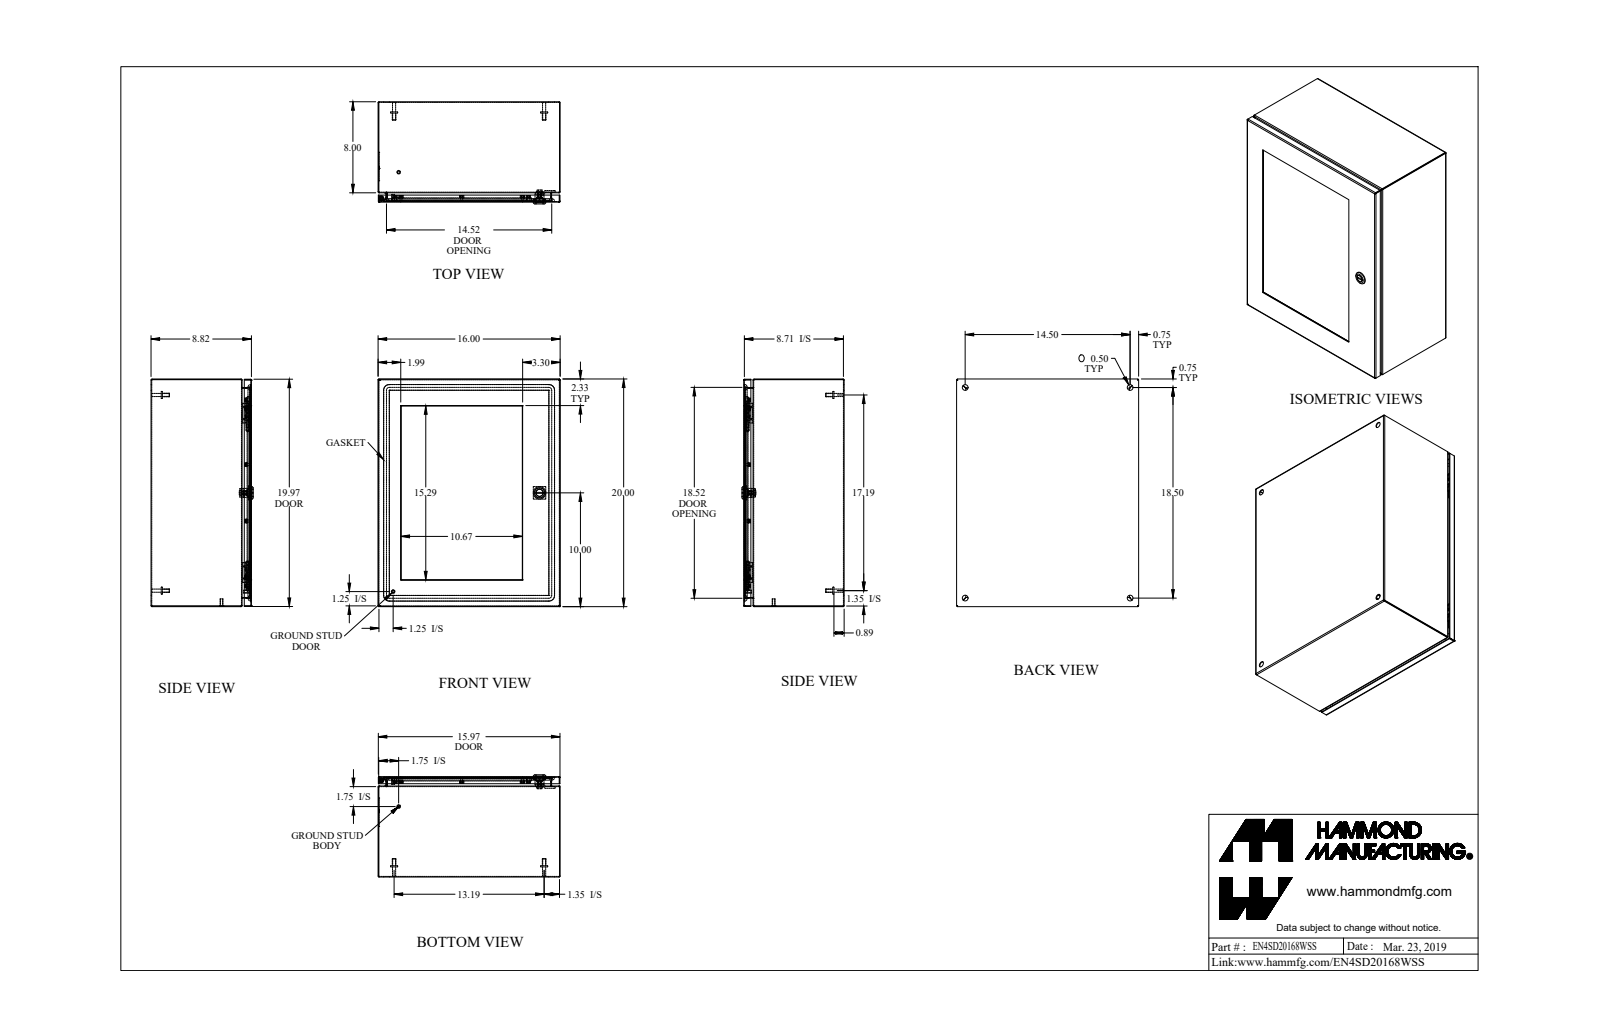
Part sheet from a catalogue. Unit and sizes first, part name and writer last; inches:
Units: inches
Overall size (bounding box): 20 × 16 × 8.982
Round holes (diameter × count): ⌀0.13 ×14, ⌀0.25 ×14, ⌀0.5 ×5, ⌀0.172 ×1, ⌀0.197 ×1, ⌀0.24 ×1, ⌀0.242 ×1, ⌀0.387 ×1, ⌀0.63 ×1, ⌀0.768 ×1
Round bosses / shafts (diameter × count): ⌀0.226 ×15, ⌀0.368 ×14, ⌀0.164 ×14, ⌀0.313 ×6, ⌀0.625 ×5, ⌀0.275 ×4, ⌀0.25 ×2, ⌀1.1 ×1
Partial cylindrical surfaces — rounded edges, fillets, slot ends (radius × count): R0.029 ×21, R0.086 ×21, R0.188 ×12, R0.125 ×10, R0.006 ×4, R0.016 ×4, R0.062 ×4, R0.088 ×4
Main face-to-face distances: 0.057, 8.765, 8.708, 15.943, 19.943, 0.25, 8.458, 8.515, 15.886, 16
Hole centre spacings: 4.958, 15.612, 15.614, 5.335, 9.917, 12.551, 12.714, 12.716
Volume: 124.5 in³ · Surface area: 3 094 in²
Bodies: 59 solids, 1220 faces (612 planar, 368 cylindrical, 240 other)
Part name (STEP PRODUCT): EN4SD20168WSS_Default
STEP written by: SolidWorks 2019 (CONFIG_CONTROL_DESIGN)
